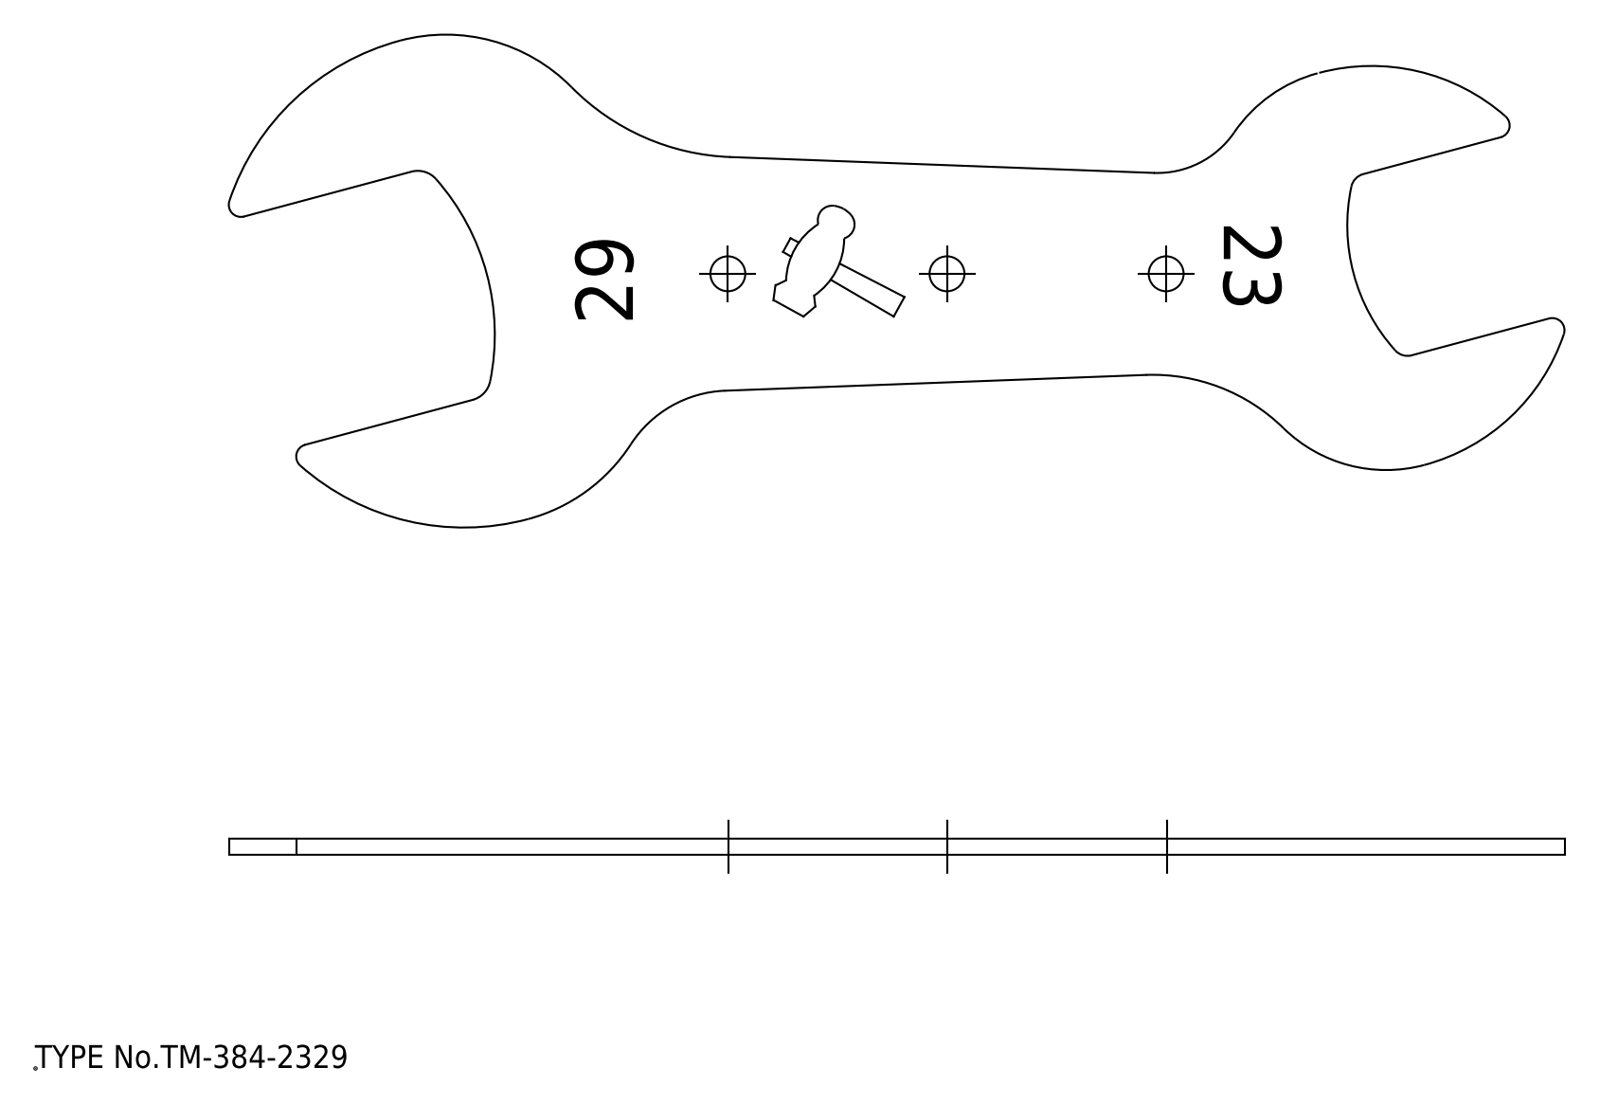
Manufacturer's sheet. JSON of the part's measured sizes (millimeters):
{"step_written_by": "spGate 19.8.4 (****-****-****-****) (AUTOMOTIVE_DESIGN)", "units": "millimeters", "bodies": {"solids": 1, "faces": 36, "planar": 8, "cylindrical": 28, "other": 0}, "overall_size": [164.56, 60.7, 2], "volume_mm3": 9577, "surface_area_mm2": 10659, "round_holes": [[4.3, 3]], "partial_cylinders_radius": [[1.5, 4], [2, 2], [3, 2], [18.1, 2], [21.8, 2], [23, 2], [29, 2], [11.5, 1]], "face_to_face_distances": [2, 29.11, 53.77, 24.66, 30.66, 1.55, 23.11], "hole_center_spacings": [27, 54]}
